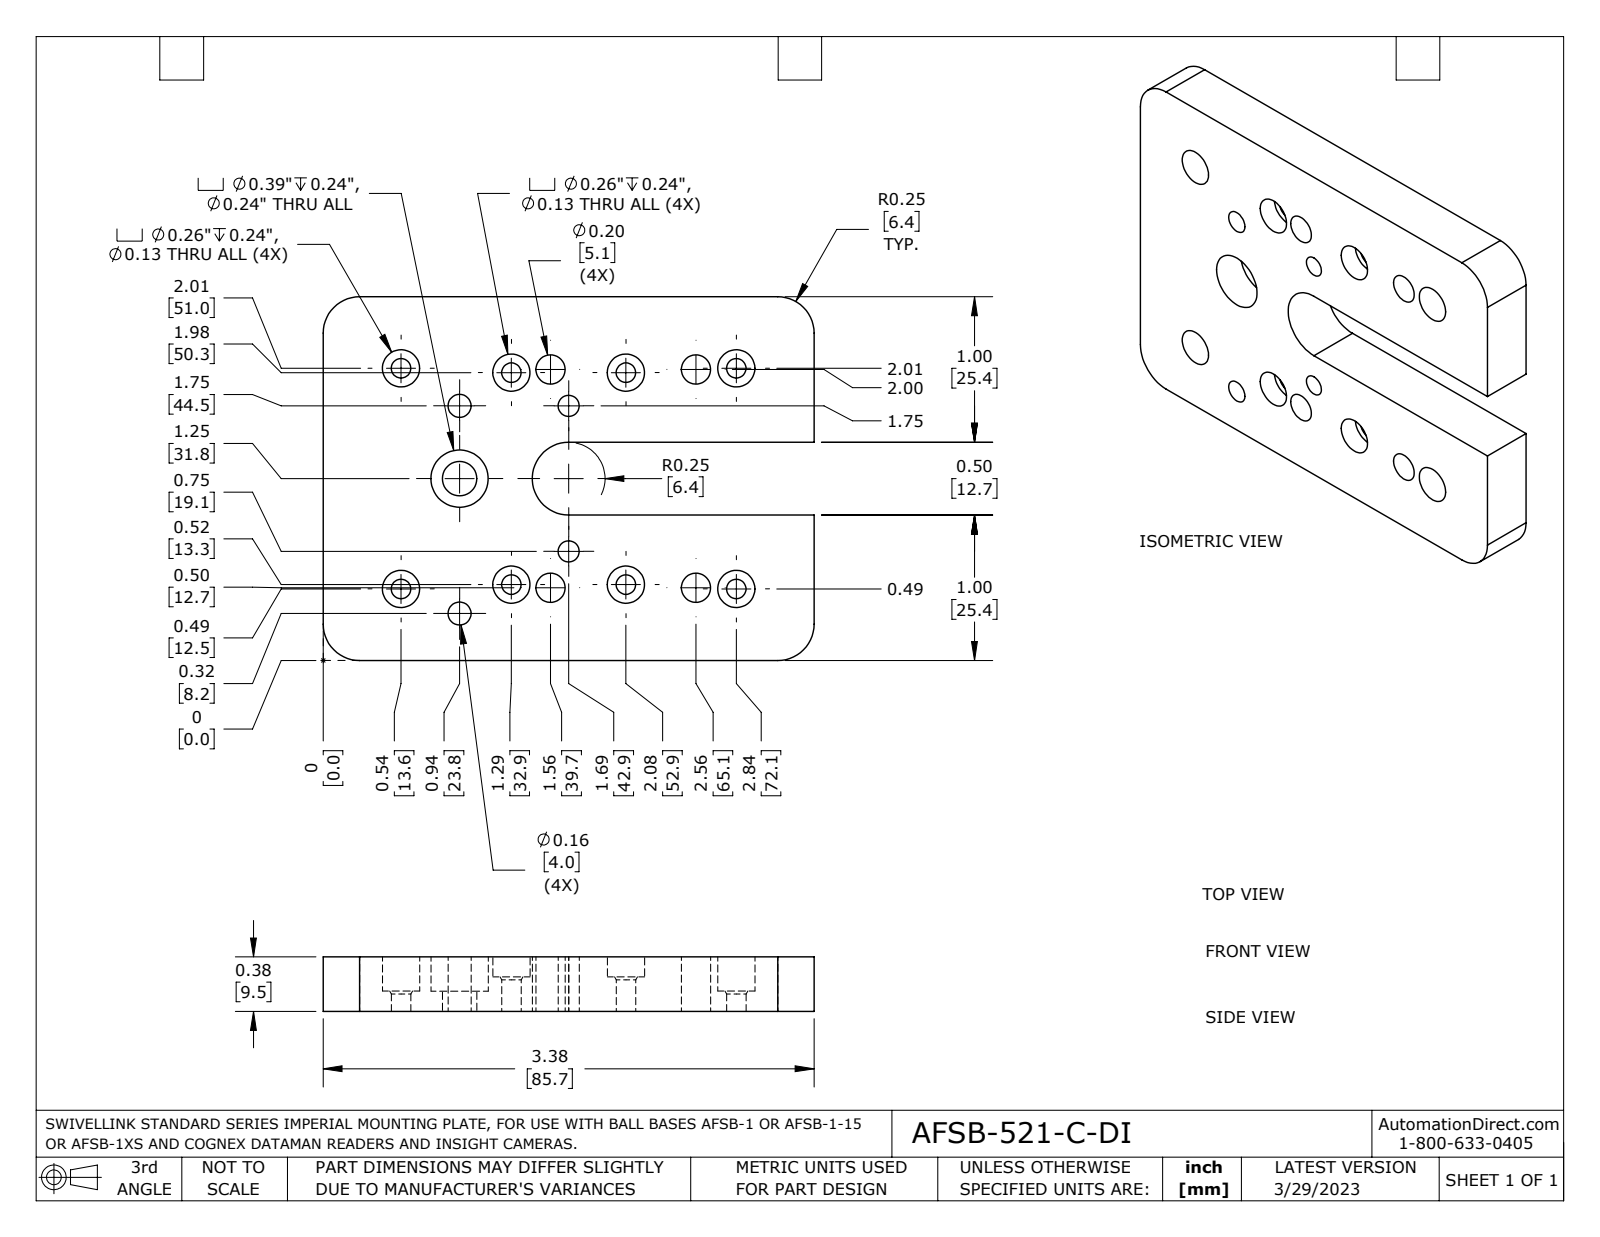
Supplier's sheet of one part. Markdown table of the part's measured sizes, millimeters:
| quantity | value |
| --- | --- |
| part name | AFSB-521-C-DI |
| STEP written by | SolidWorks 2021 (AUTOMOTIVE_DESIGN) |
| units | millimeters |
| bodies | 1 solid, 61 faces (22 planar, 31 cylindrical, 8 other) |
| overall size | 85.7 × 63.5 × 9.5 |
| volume | 42 620 mm³ |
| surface area | 15 460 mm² |
| round holes (diameter × count) | 3.4 × 8, 6.5 × 8, 5.1 × 4, 3.7 × 2, 4 × 2, 6 × 1, 10 × 1 |
| partial cylindrical surfaces (radius × count) | 6.4 × 5 |
| main face-to-face distances | 9.5, 25.4, 38.1, 63.5, 12.7, 85.7, 6, 3.5, 3.6, 2.5 |
| hole center spacings | 11.6, 19.3, 30, 32.8, 39.3, 42.4, 43.3, 54.5 |
